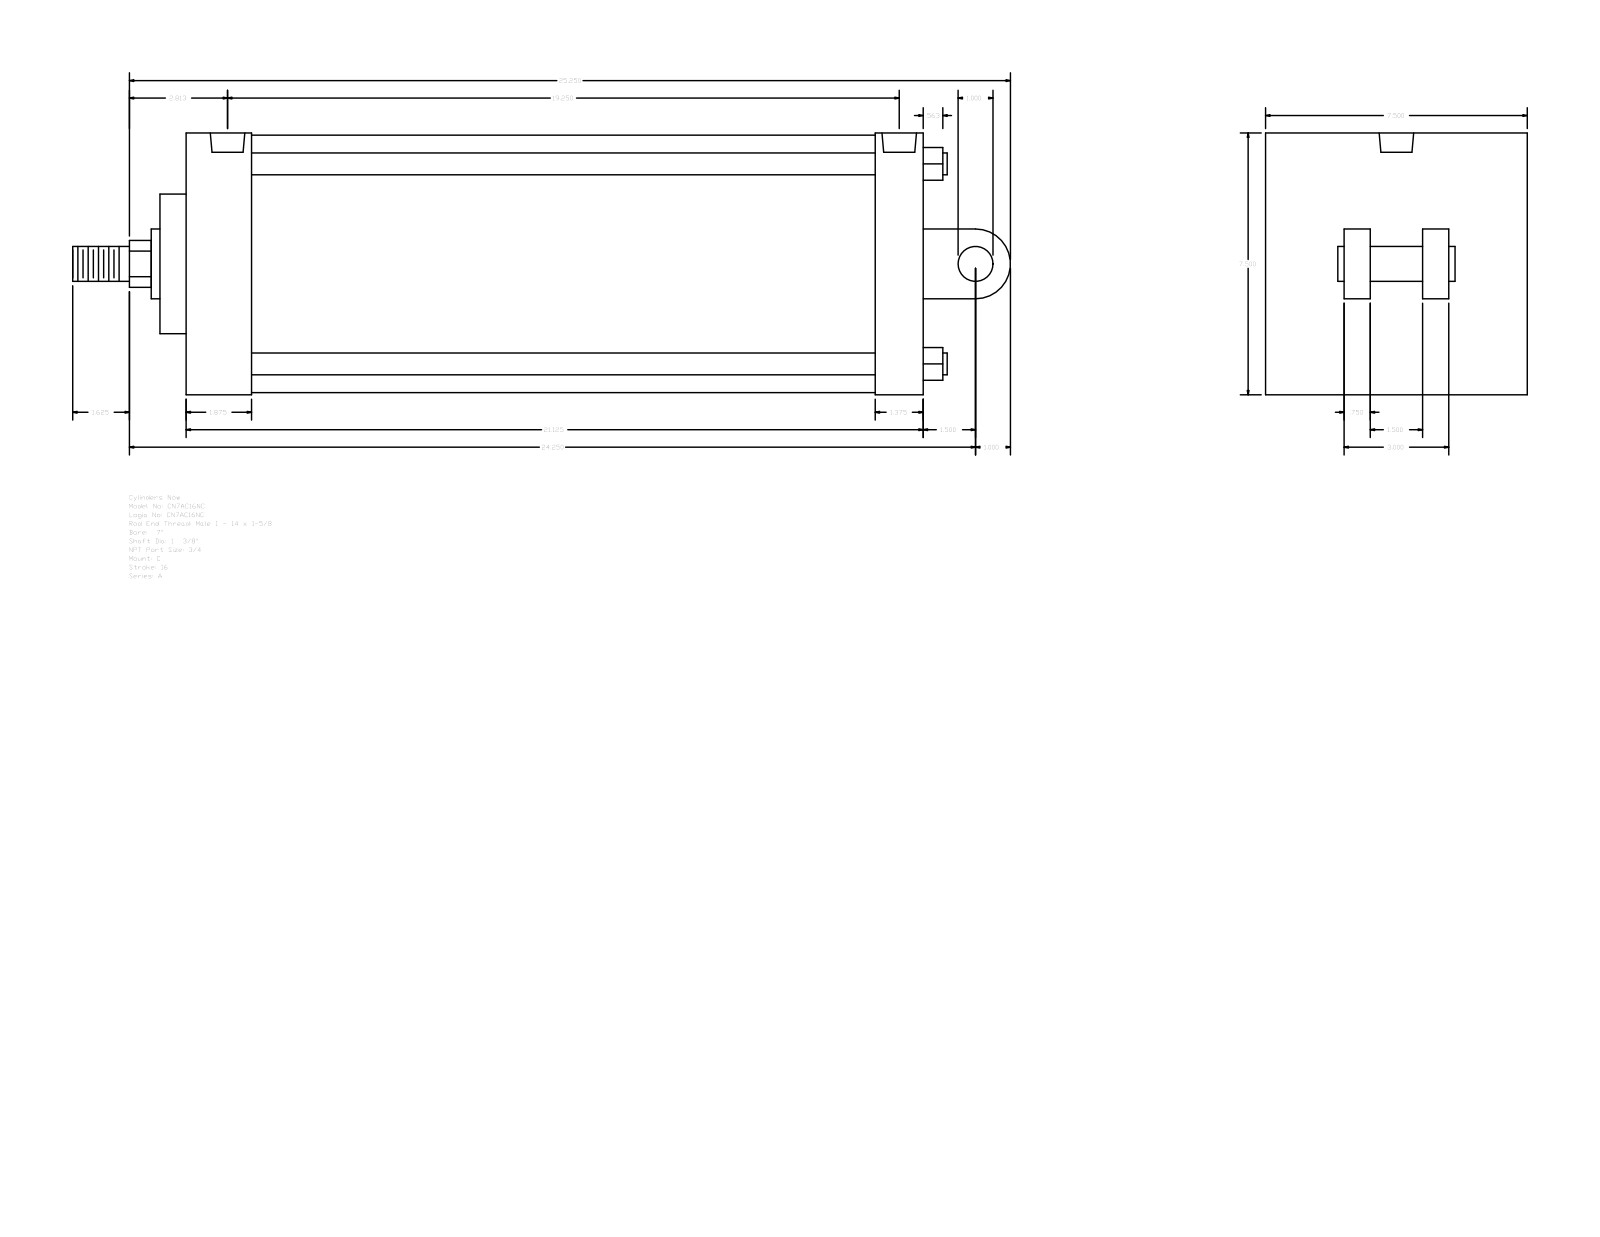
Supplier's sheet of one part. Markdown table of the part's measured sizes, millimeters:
| quantity | value |
| --- | --- |
| part name | A_C__0700_1.375 |
| STEP written by | GSSL Pune (CONFIG_CONTROL_DESIGN) |
| units | millimeters |
| bodies | 0 solids, 104 faces (75 planar, 29 cylindrical, 0 other) |
| overall size | 682.62 × 190.5 × 190.5 |
| round holes (diameter × count) | 15.08 × 4, 25.12 × 2 |
| round bosses / shafts (diameter × count) | 15.88 × 4, 25.4 × 2, 187.32 × 1, 50.8 × 1, 34.92 × 1 |
| partial cylindrical surfaces (radius × count) | 17.06 × 1, 25.4 × 1 |
| main face-to-face distances | 190.5, 536.58, 76.2, 57.15, 19.04, 555.62, 66.67, 47.63, 488.95, 520.69 |
| hole center spacings | 5.56, 477.83, 483.39, 488.95 |
